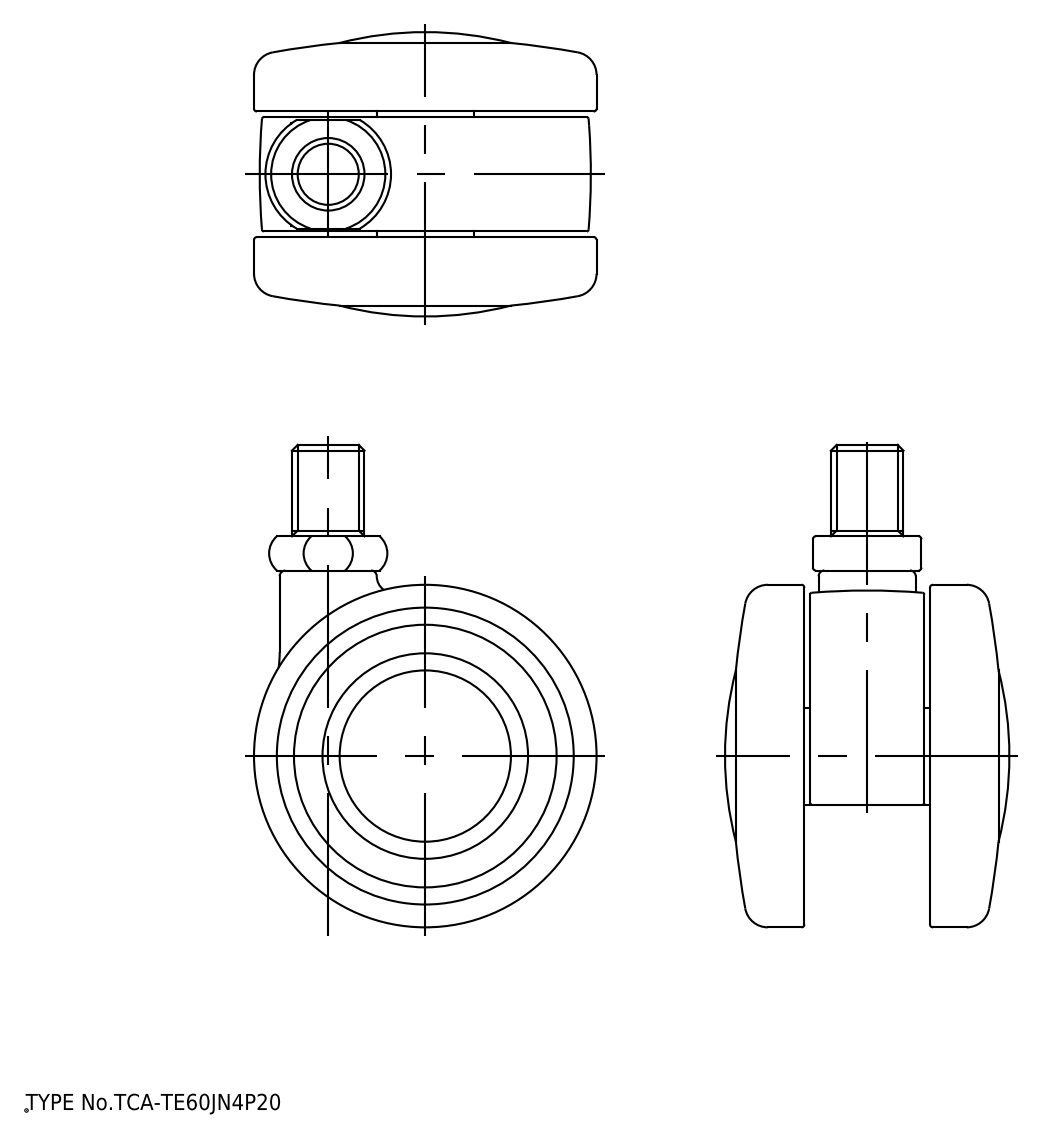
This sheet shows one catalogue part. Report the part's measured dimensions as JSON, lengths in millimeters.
{"part_name": "TCA-TE60J_Body; TCA-TE60J_Wheel; TCA-TE60JN4P20_Shaft", "step_written_by": "spGate 18.9.1 (****-****-****-****) (AUTOMOTIVE_DESIGN)", "units": "millimeters", "bodies": {"solids": 4, "faces": 185, "planar": 46, "cylindrical": 73, "other": 66}, "overall_size": [84.5, 60, 49.14], "volume_mm3": 87144, "surface_area_mm2": 32087, "round_holes": [[8, 1], [9.3, 1], [10.7, 1], [20, 1], [30.2, 1], [45, 1]], "round_bosses_or_shafts": [[60, 1], [36, 1], [29.9, 1], [18, 1], [17, 1], [12.7, 1], [10.5, 1], [6.5, 1]], "partial_cylinders_radius": [[0.3, 5], [1, 3], [2, 3], [10.5, 1], [26.5, 1], [29, 1]], "face_to_face_distances": [2, 19, 7, 5, 24, 26, 11, 30.5, 0.5, 28.5]}
